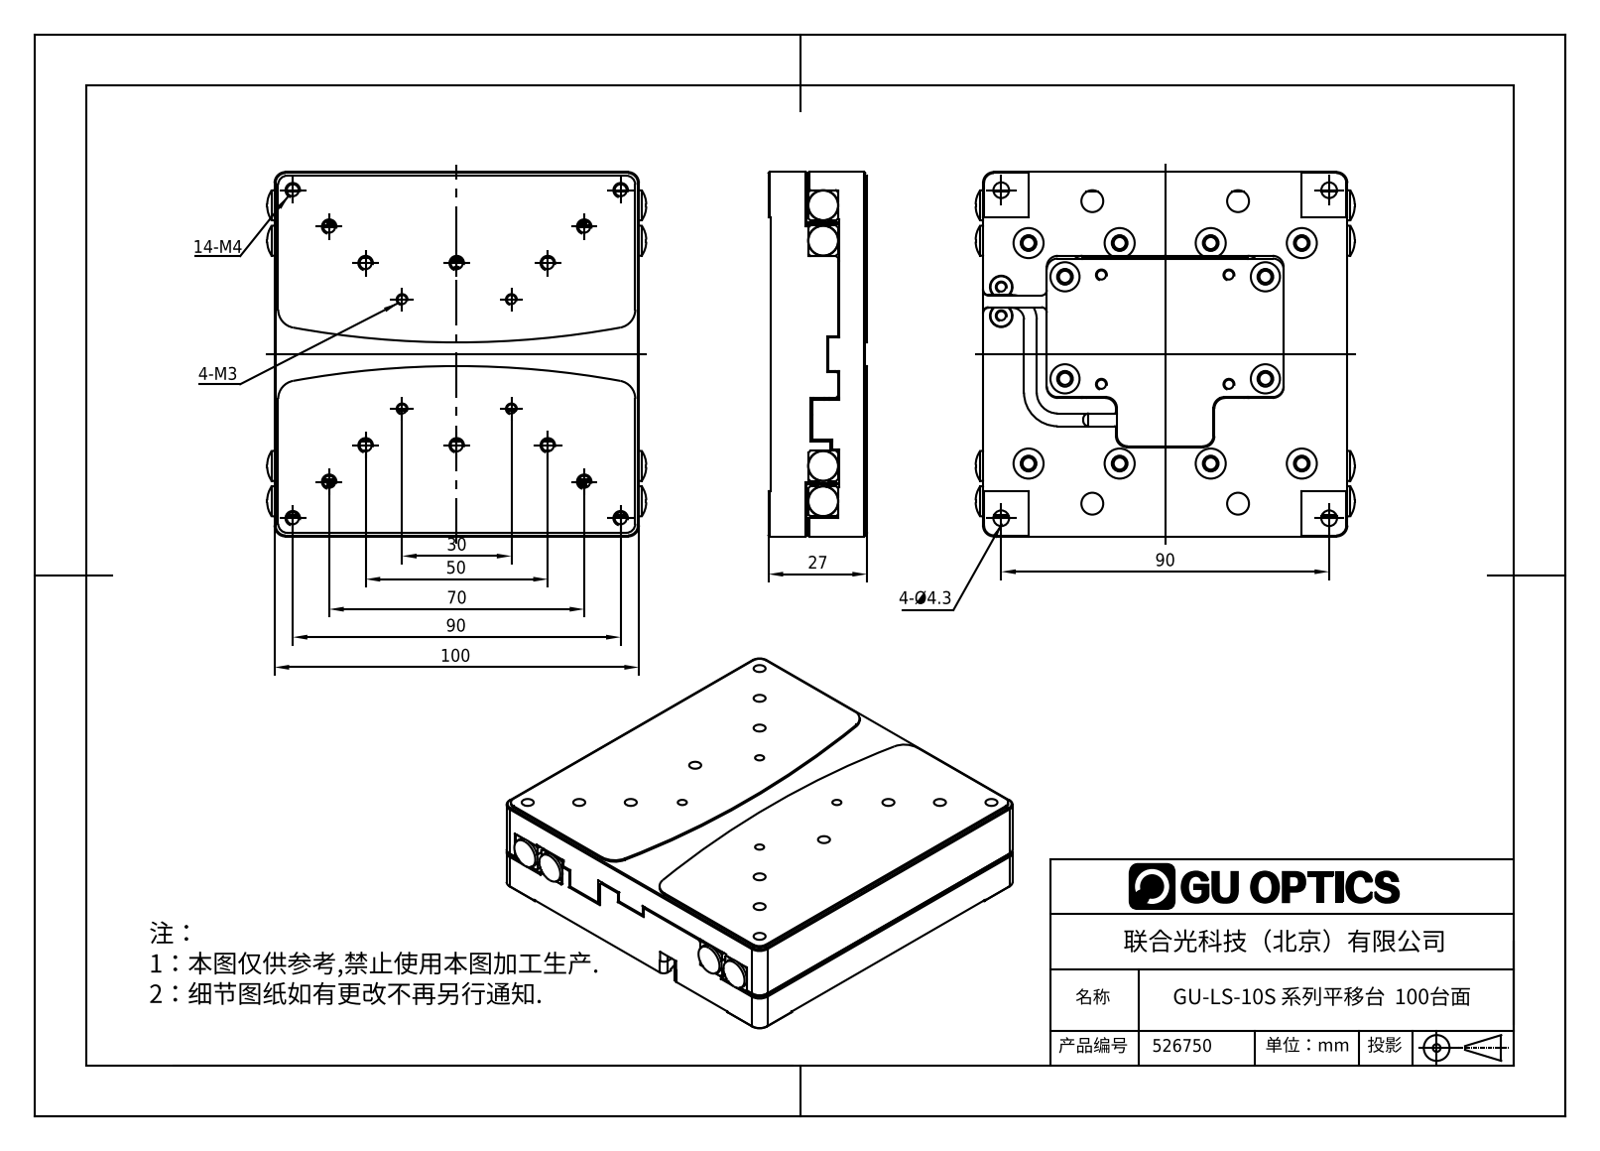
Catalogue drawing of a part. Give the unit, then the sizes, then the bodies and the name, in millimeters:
Units: millimetres
Overall size (bounding box): 104.01 × 100 × 27
Round holes (diameter × count): ⌀3.3 ×34, ⌀2.5 ×26, ⌀3 ×22, ⌀6 ×20, ⌀4 ×18, ⌀4.3 ×16, ⌀8 ×8, ⌀8.25 ×8, ⌀2.05 ×4, ⌀9 ×1
Round bosses / shafts (diameter × count): ⌀3 ×28
Partial cylindrical surfaces — rounded edges, fillets, slot ends (radius × count): R3 ×33, R2.5 ×14, R2 ×11, R1.5 ×10, R5 ×4, R3.1 ×2, R250 ×2, R3.25 ×1
Main face-to-face distances: 0.5, 8, 26.5, 4, 18.5, 16, 8.5, 7.5, 10.5, 10
Hole centre spacings: 25, 50, 65.46, 27.31, 75.74, 22.06, 60.5, 61.72
Bodies: 0 solids, 1505 faces (690 planar, 464 cylindrical, 351 other)
Part name (STEP PRODUCT): GU-LS-10S 系列平移台 100台面
STEP written by: SolidWorks 2016 (CONFIG_CONTROL_DESIGN)
